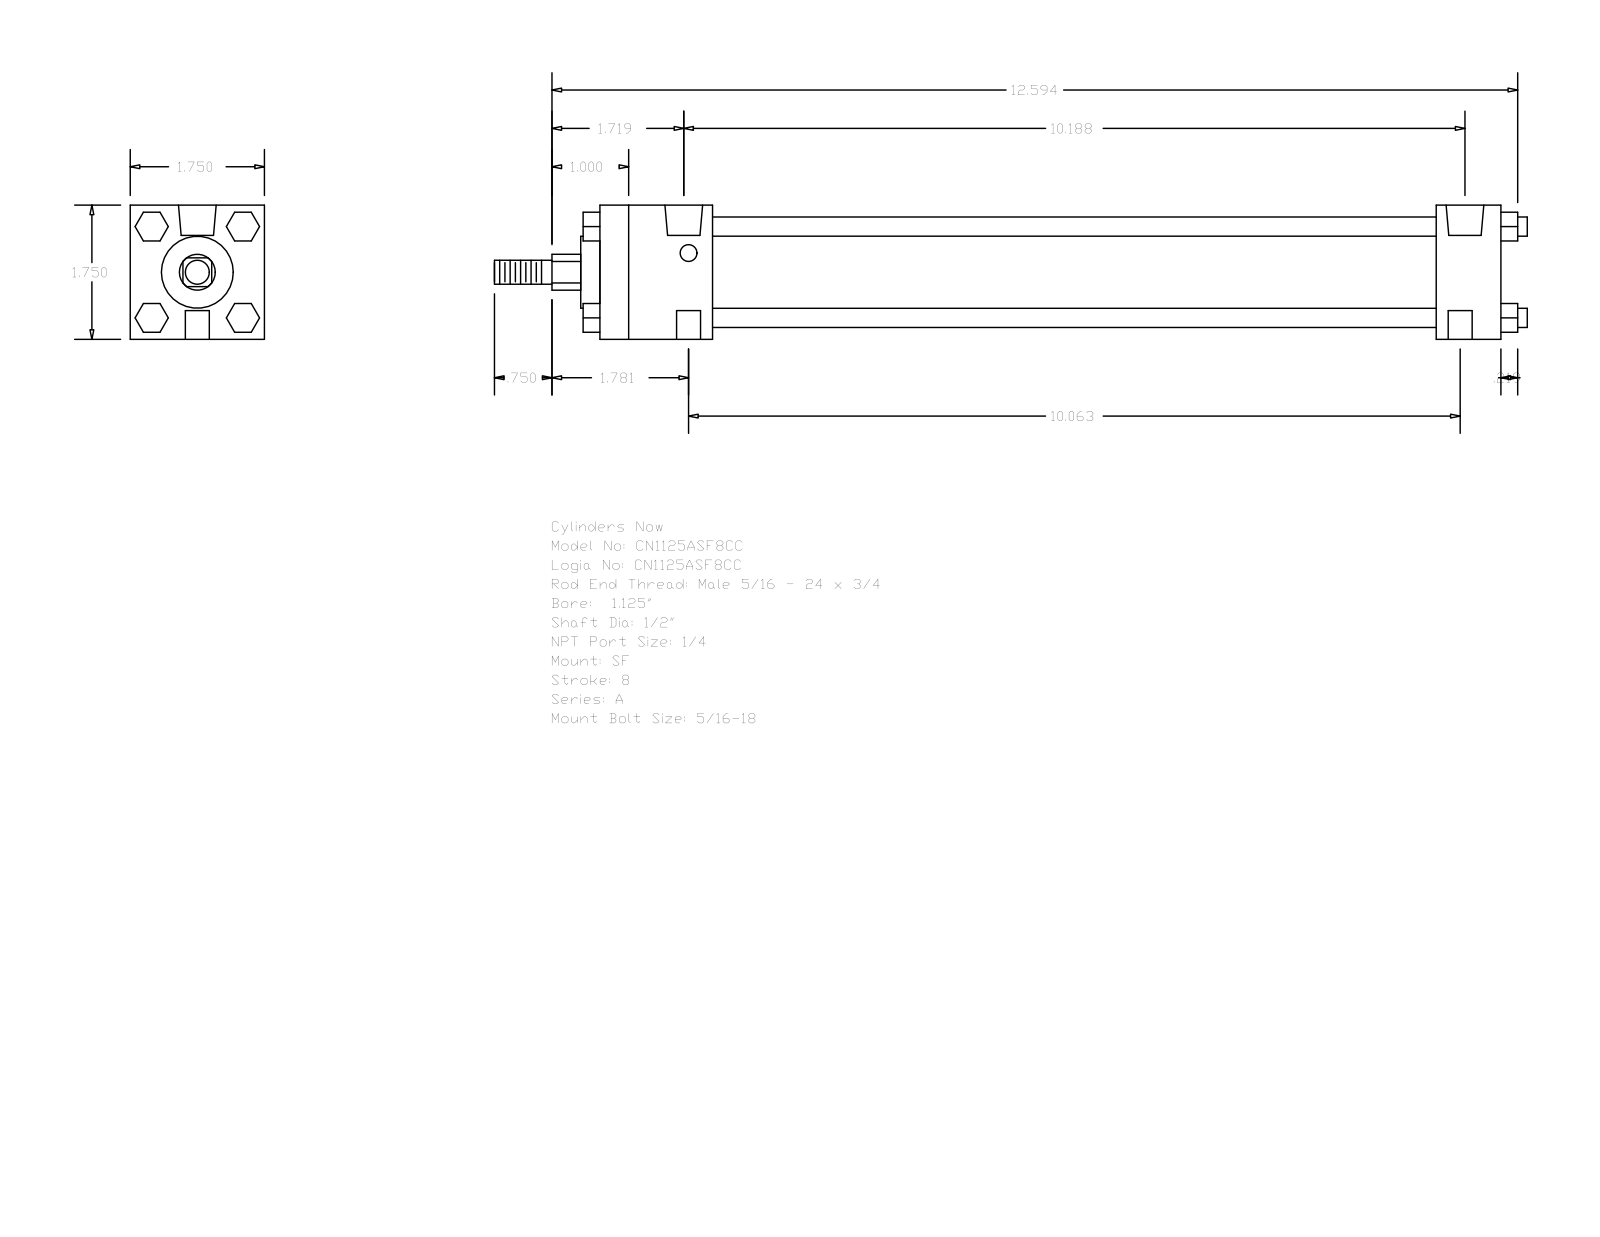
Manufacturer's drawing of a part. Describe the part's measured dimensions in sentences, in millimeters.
The part is named "A_SF__0112_0.5". Its 3-D file was written by "GSSL Pune (CONFIG_CONTROL_DESIGN)". It is 0 solids with 120 faces: 92 planar, 28 cylindrical and 0 other. Overall it measures 342.11 by 44.45 by 44.45 millimeters. Round holes: 2 of diameter 5.56, 2 of diameter 7.94, 2 of diameter 12.49. Round bosses or shafts: 4 of diameter 6.35, 1 of diameter 31.88, 1 of diameter 23.81, 1 of diameter 12.7, 1 of diameter 7.94. Partial cylindrical surfaces (rounded edges, fillets, slot ends): 1 of radius 5.94. The main face-to-face distances are 44.46, 298.44, 277.01, 21.43, 37.3, 239.71, 261.14, 9.53, 5.59, 5.56. The hole center spacings are 255.59, 1.58, 1.59, 257.17, 257.18, 258.76.
